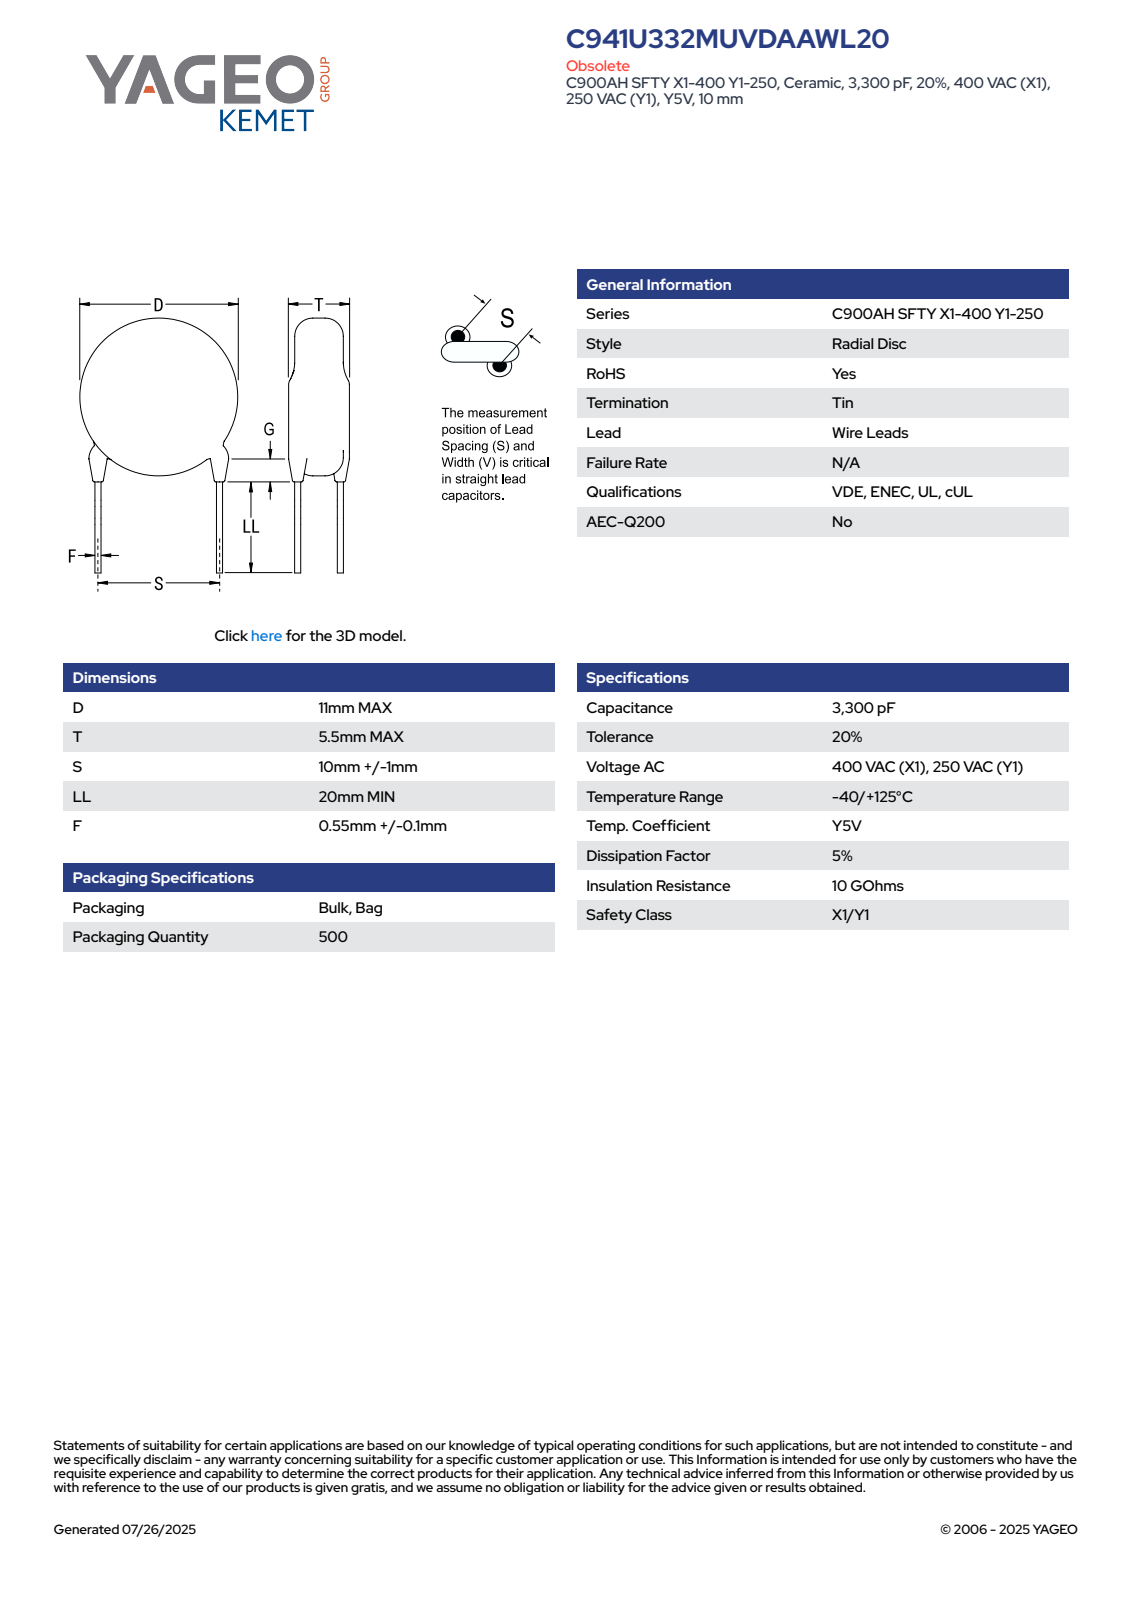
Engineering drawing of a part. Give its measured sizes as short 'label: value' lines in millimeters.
name: CCD_STC900_D11T5.5S10LL20F0.65G3
written by: SolidWorks 2014 (AUTOMOTIVE_DESIGN)
unit: mm
bodies: 4 solids, 83 faces (61 planar, 6 cylindrical, 16 other)
size: 31.34 × 11 × 5.5
volume: 525 mm³; area: 453 mm²
bosses: 2× ⌀0.65, 1× ⌀11
face distances: 5.5, 1.27, 26.47, 25.2, 0.35, 1.03, 5.19, 0.79, 3.77, 3.92
